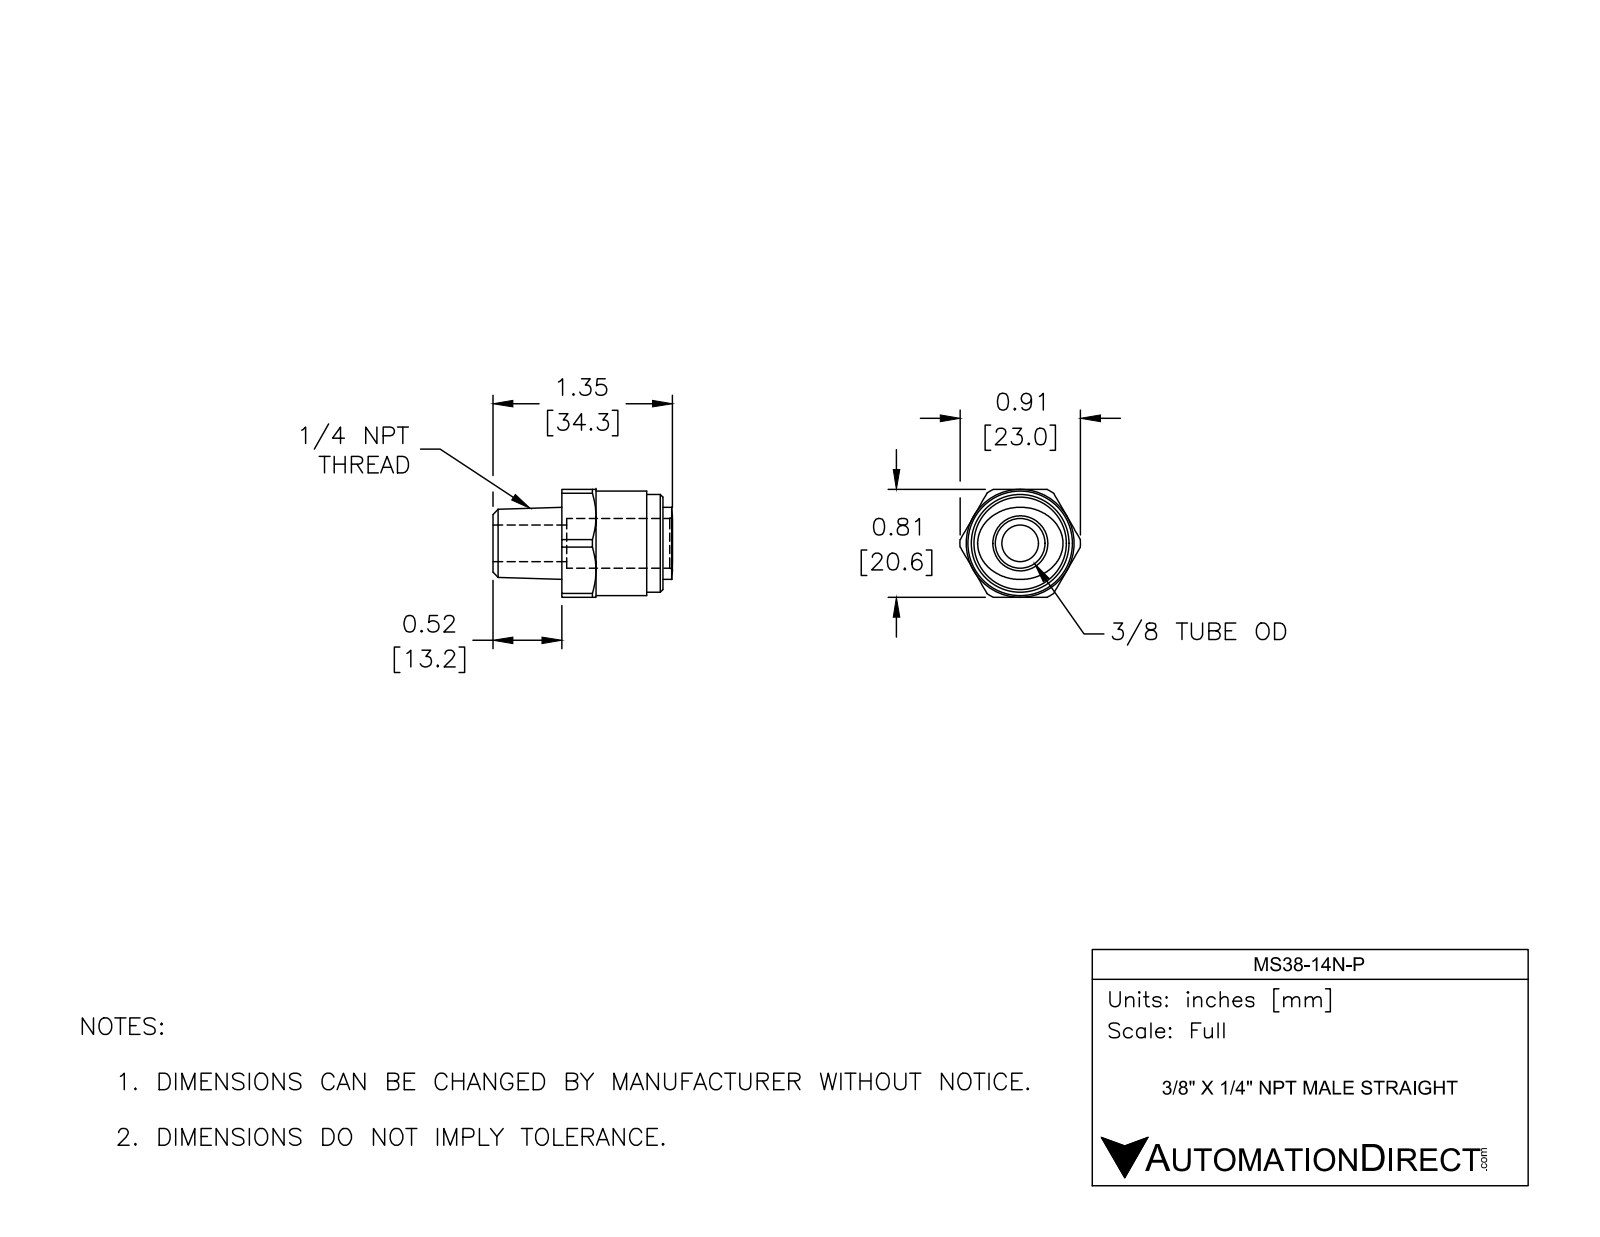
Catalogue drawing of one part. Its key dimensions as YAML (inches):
part_name: "MS38-14N-P"
step_written_by: "SolidWorks 2017 (AUTOMOTIVE_DESIGN)"
units: inches
bodies: {solids: 1, faces: 46, planar: 12, cylindrical: 15, other: 19}
overall_size: [1.35, 0.906, 0.811]
volume: 0.393
surface_area: 5.218
round_holes:
  - {diameter: 0.276, count: 1}
  - {diameter: 0.374, count: 1}
round_bosses_or_shafts:
  - {diameter: 0.787, count: 1}
  - {diameter: 0.736, count: 1}
partial_cylinders:
  - {radius: 0.453, count: 1}
face_to_face_distances: [0.811, 0.76, 0.52, 1.28, 1.157, 0.638, 0.122, 0.555, 0.035, 0.602]
